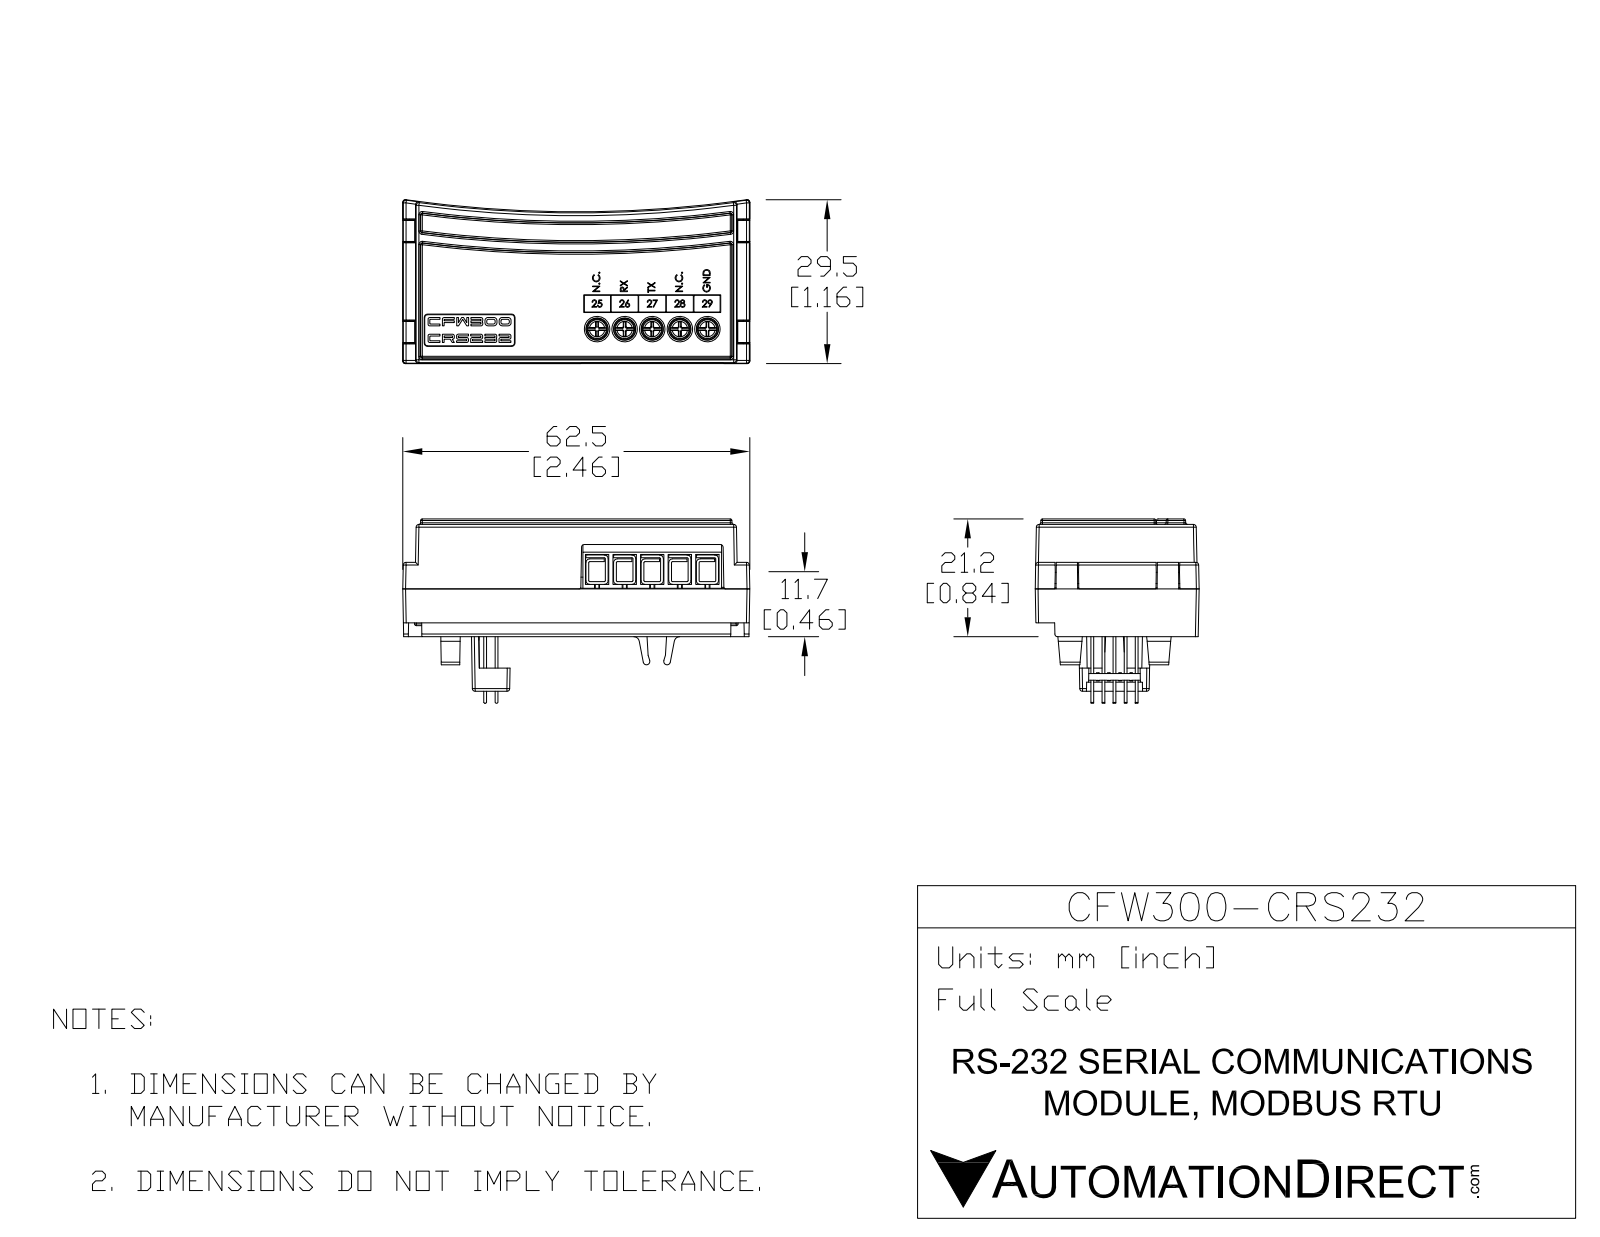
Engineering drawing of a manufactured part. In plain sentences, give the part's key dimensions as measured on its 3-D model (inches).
The part is named "CFW300-CRS232". Its 3-D file was written by "SolidWorks 2017 (AUTOMOTIVE_DESIGN)". It is 1 solid with 713 faces: 316 planar, 31 cylindrical and 366 other. Overall it measures 2.461 by 1.159 by 0.835 inches. Its volume is 2.164 cubic inches and its surface area 11.46 square inches. Round holes: 5 of diameter 0.181. Partial cylindrical surfaces (rounded edges, fillets, slot ends): 11 of radius 0.039, 4 of radius 0.02, 4 of radius 0.024, 1 of radius 8.543. The main face-to-face distances are 0.835, 0.091, 2.37, 2.461, 0.098, 0.737, 2.28, 0.134, 0.528, 0.43. The hole center spacings are 0.196, 0.391, 0.587, 0.783.
